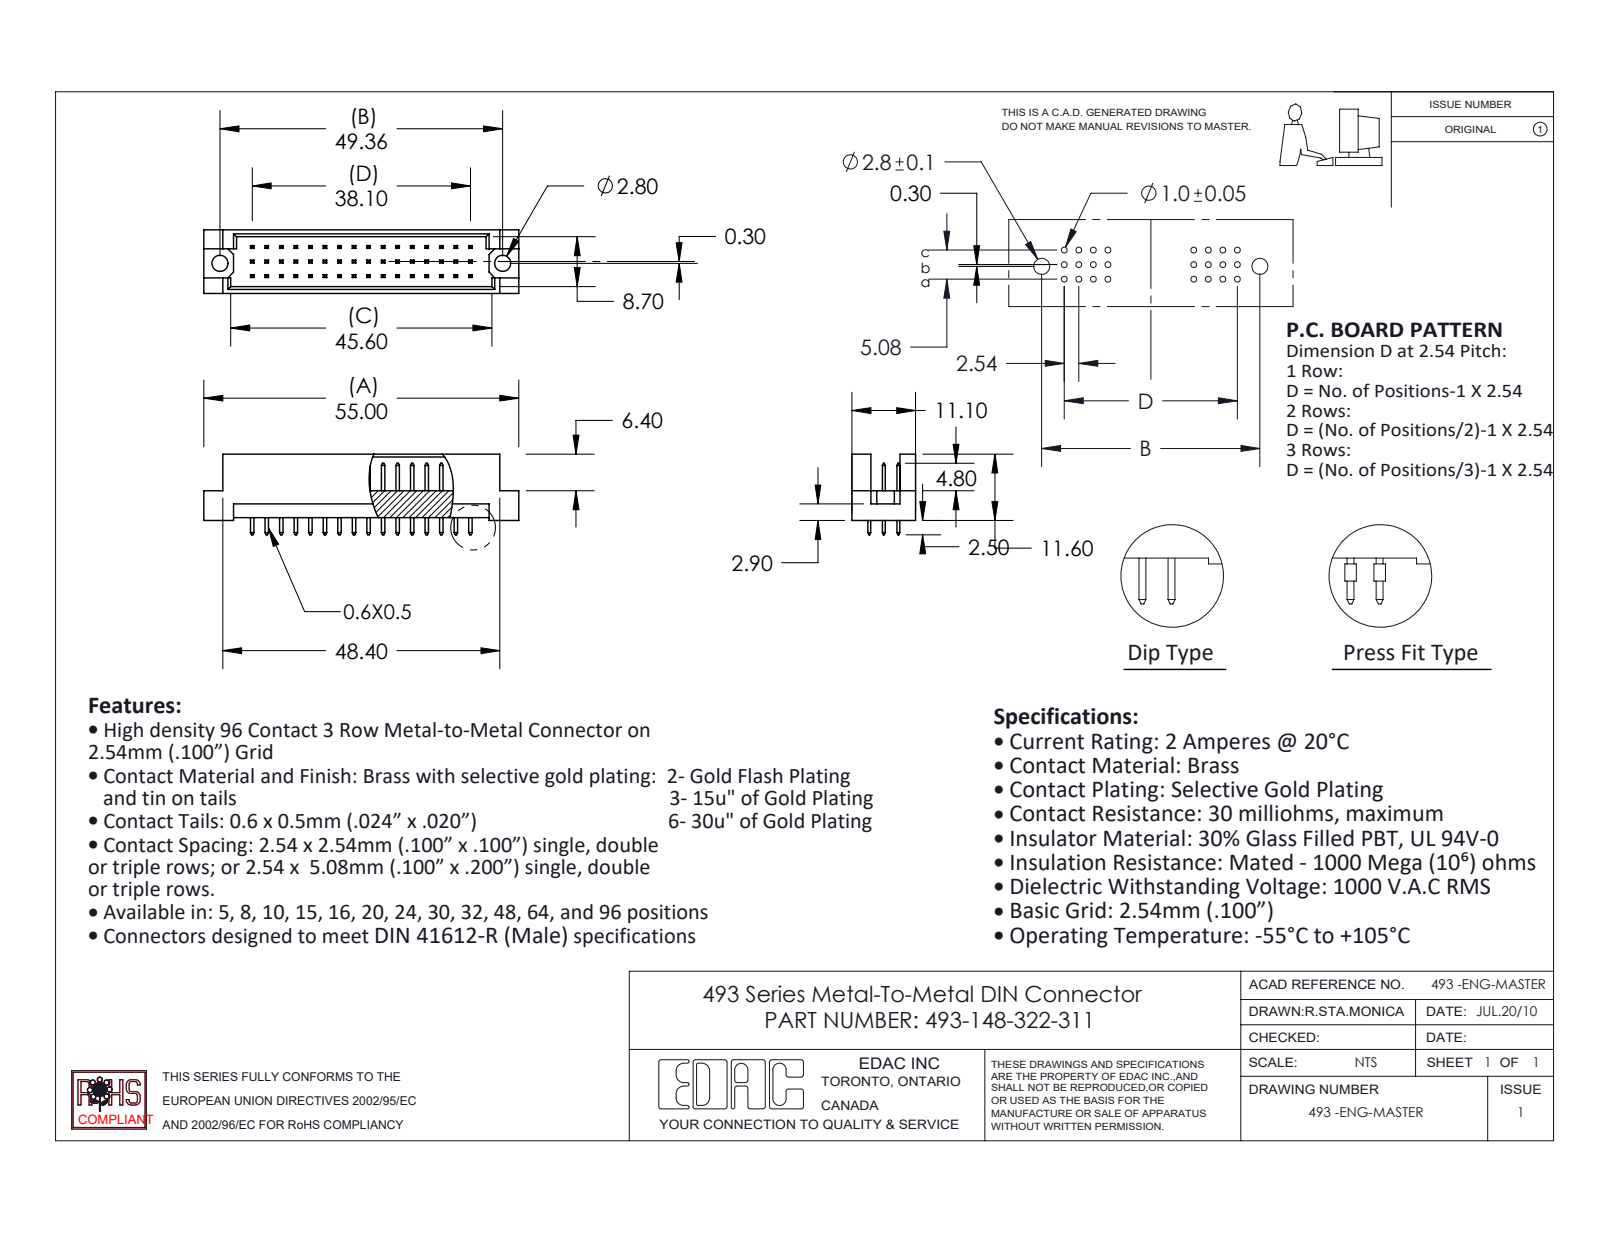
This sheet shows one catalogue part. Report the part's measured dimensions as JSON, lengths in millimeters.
{"part_name": "493-290_22; 493 Part_48; 493-148-322-311", "step_written_by": "SolidWorks 2020 (CONFIG_CONTROL_DESIGN)", "units": "millimeters", "bodies": {"solids": 49, "faces": 916, "planar": 912, "cylindrical": 4, "other": 0}, "overall_size": [55, 14.1, 11.1], "volume_mm3": 3447, "surface_area_mm2": 5058, "round_holes": [[2.8, 2]], "face_to_face_distances": [2.54, 1.2, 9.9, 5.08, 0.5, 11.1, 8.7, 4.7, 7.62, 2.76], "hole_center_spacings": [49.36]}
